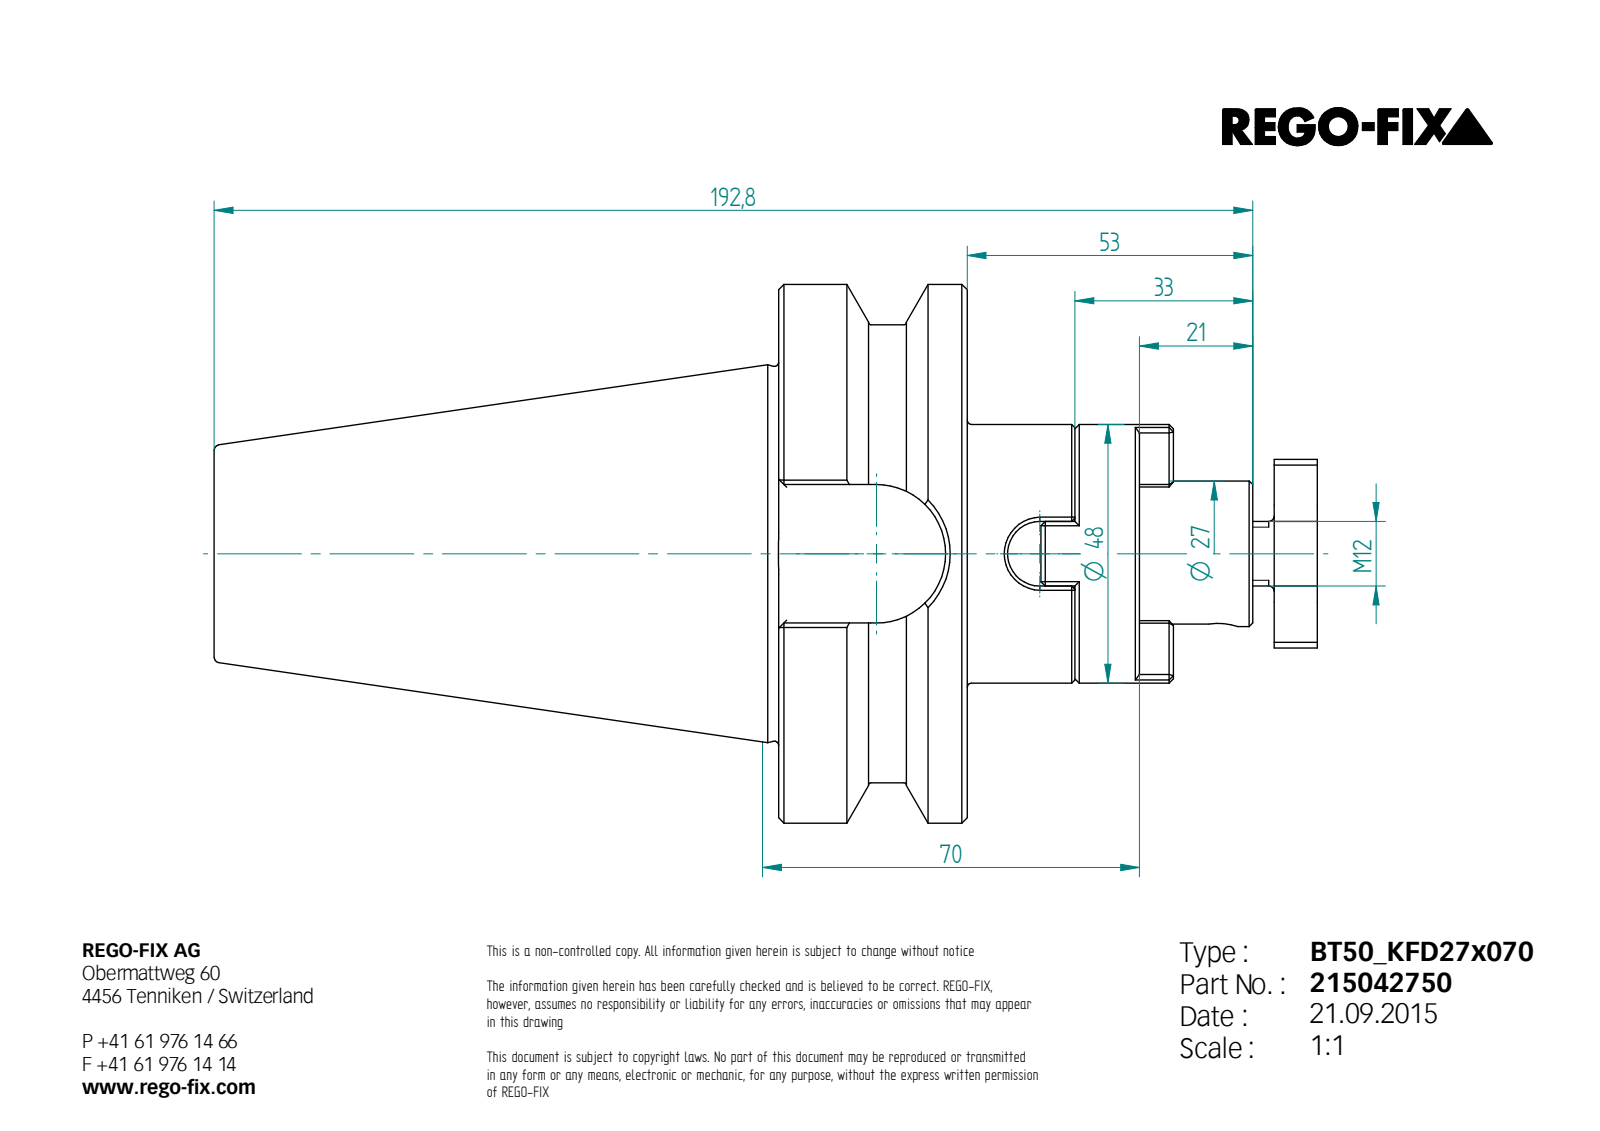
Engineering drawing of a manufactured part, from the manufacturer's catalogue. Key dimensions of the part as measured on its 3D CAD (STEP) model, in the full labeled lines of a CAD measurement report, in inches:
STEP written by: Unknown (AUTOMOTIVE_DESIGN)
Units: inches
Bodies: 3 solids, 207 faces (118 planar, 35 cylindrical, 54 other)
Overall size (bounding box): 8.063 × 3.937 × 3.937
Volume: 31.52 in³ · Surface area: 109.9 in²
Round holes (diameter × count): ⌀0.398 ×1, ⌀0.512 ×1, ⌀0.817 ×1, ⌀0.984 ×1, ⌀1.063 ×1
Round bosses / shafts (diameter × count): ⌀3.937 ×1, ⌀3.346 ×1, ⌀1.89 ×1, ⌀1.039 ×1, ⌀0.472 ×1
Partial cylindrical surfaces — rounded edges, fillets, slot ends (radius × count): R0.02 ×4, R0.118 ×4, R0.138 ×2, R0.236 ×1, R0.506 ×1, R0.689 ×1
Main face-to-face distances: 1.378, 0.787, 0.472, 2.165, 1.299, 1.26, 2.638, 0.315, 2.783, 3.937
